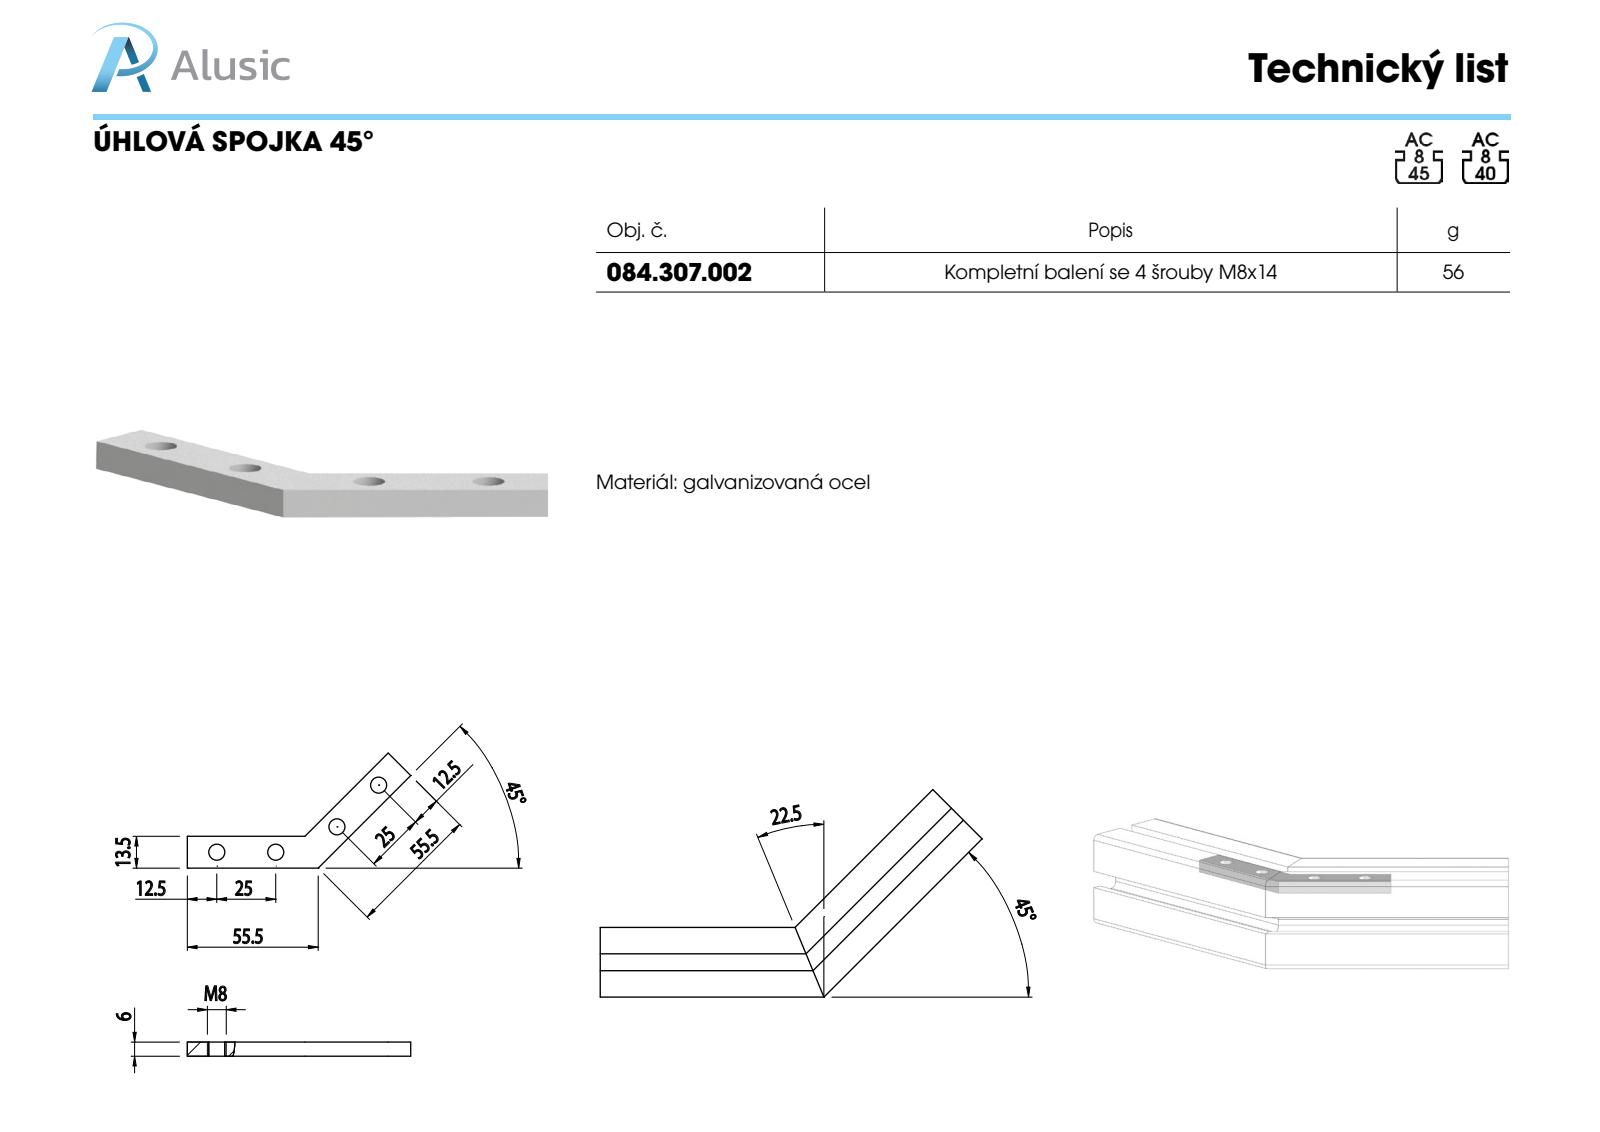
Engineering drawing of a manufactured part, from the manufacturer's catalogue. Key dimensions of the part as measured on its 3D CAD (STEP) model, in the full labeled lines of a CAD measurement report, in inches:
Part name (STEP PRODUCT): 084.307.002
STEP written by: SolidWorks 2011 (CONFIG_CONTROL_DESIGN)
Units: inches
Bodies: 1 solid, 16 faces (8 planar, 8 cylindrical, 0 other)
Overall size (bounding box): 3.73 × 1.921 × 0.236
Volume: 0.468 in³ · Surface area: 6.967 in²
Round holes (diameter × count): ⌀0.268 ×4
Main face-to-face distances: 0.236, 0.531
Hole centre spacings: 0.984, 1.106, 2.05, 2.05, 2.925
